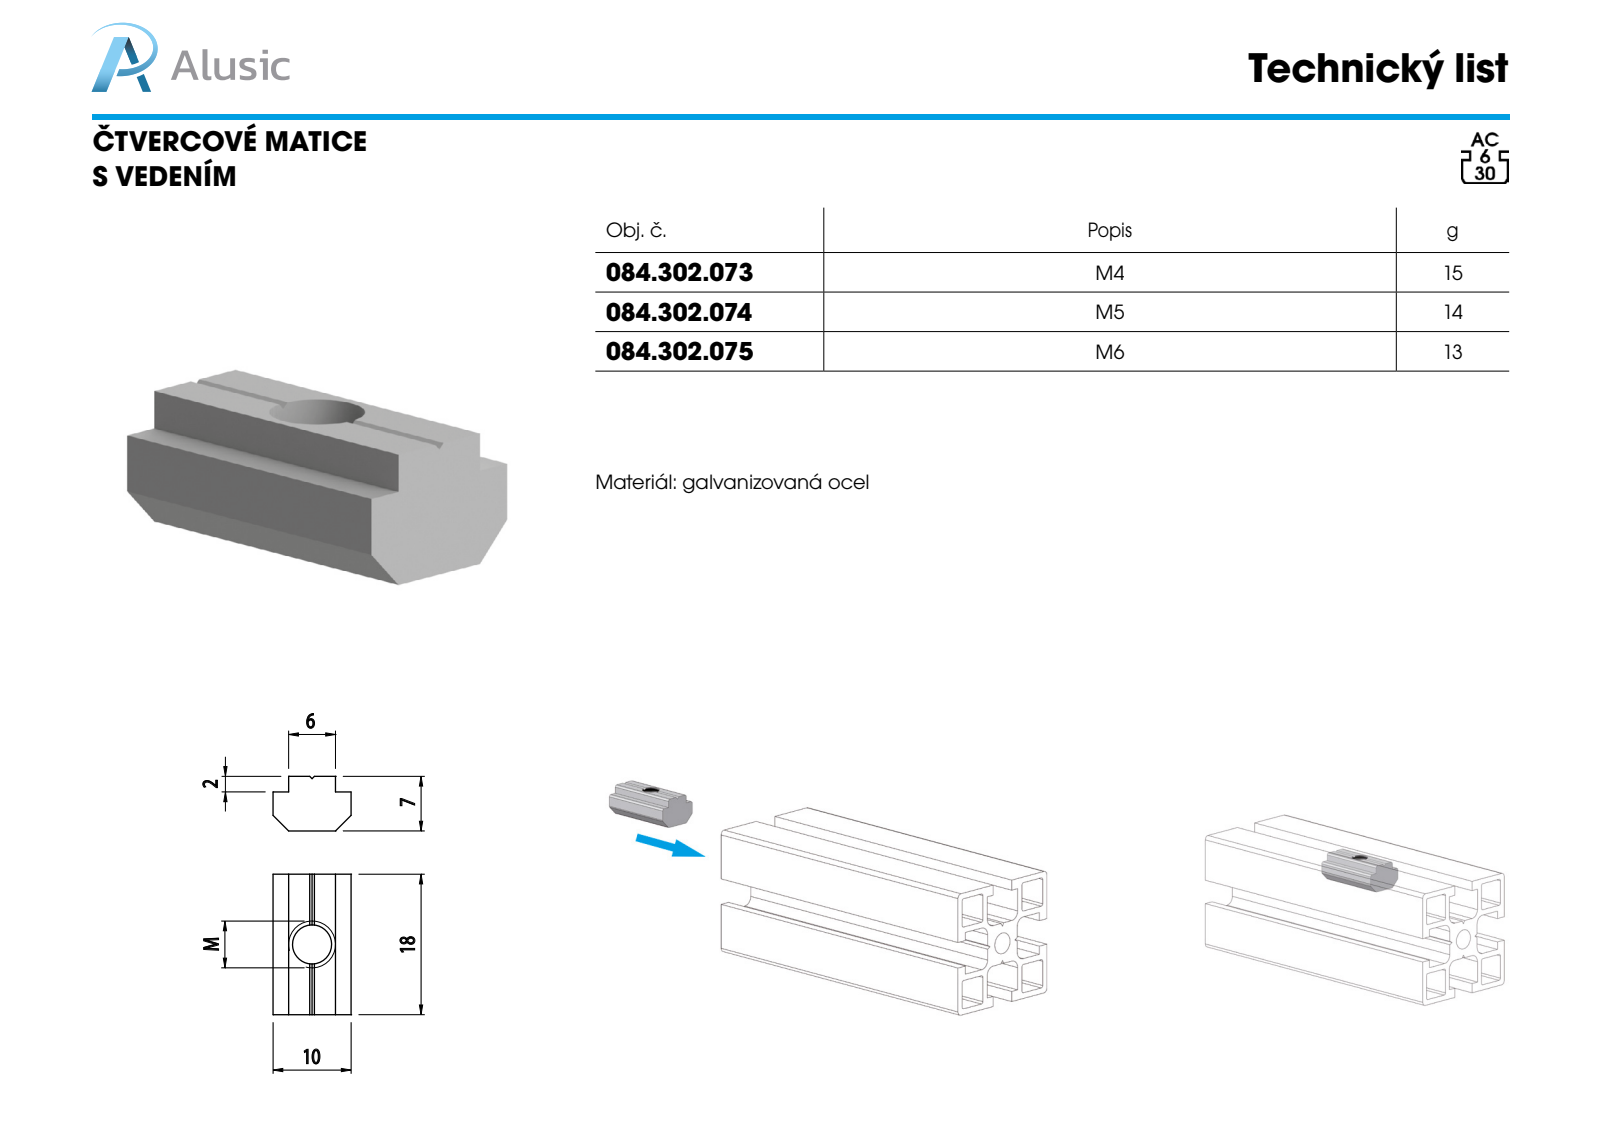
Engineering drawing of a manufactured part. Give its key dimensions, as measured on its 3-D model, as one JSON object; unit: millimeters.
{"part_name": "084.302.075", "step_written_by": "SolidWorks 2012 (CONFIG_CONTROL_DESIGN)", "units": "millimeters", "bodies": {"solids": 1, "faces": 30, "planar": 18, "cylindrical": 8, "other": 4}, "overall_size": [18, 10, 7], "volume_mm3": 894, "surface_area_mm2": 756, "round_holes": [[5, 1]], "partial_cylinders_radius": [[0.5, 4]], "face_to_face_distances": [2, 8, 5, 7, 18, 10, 6]}
